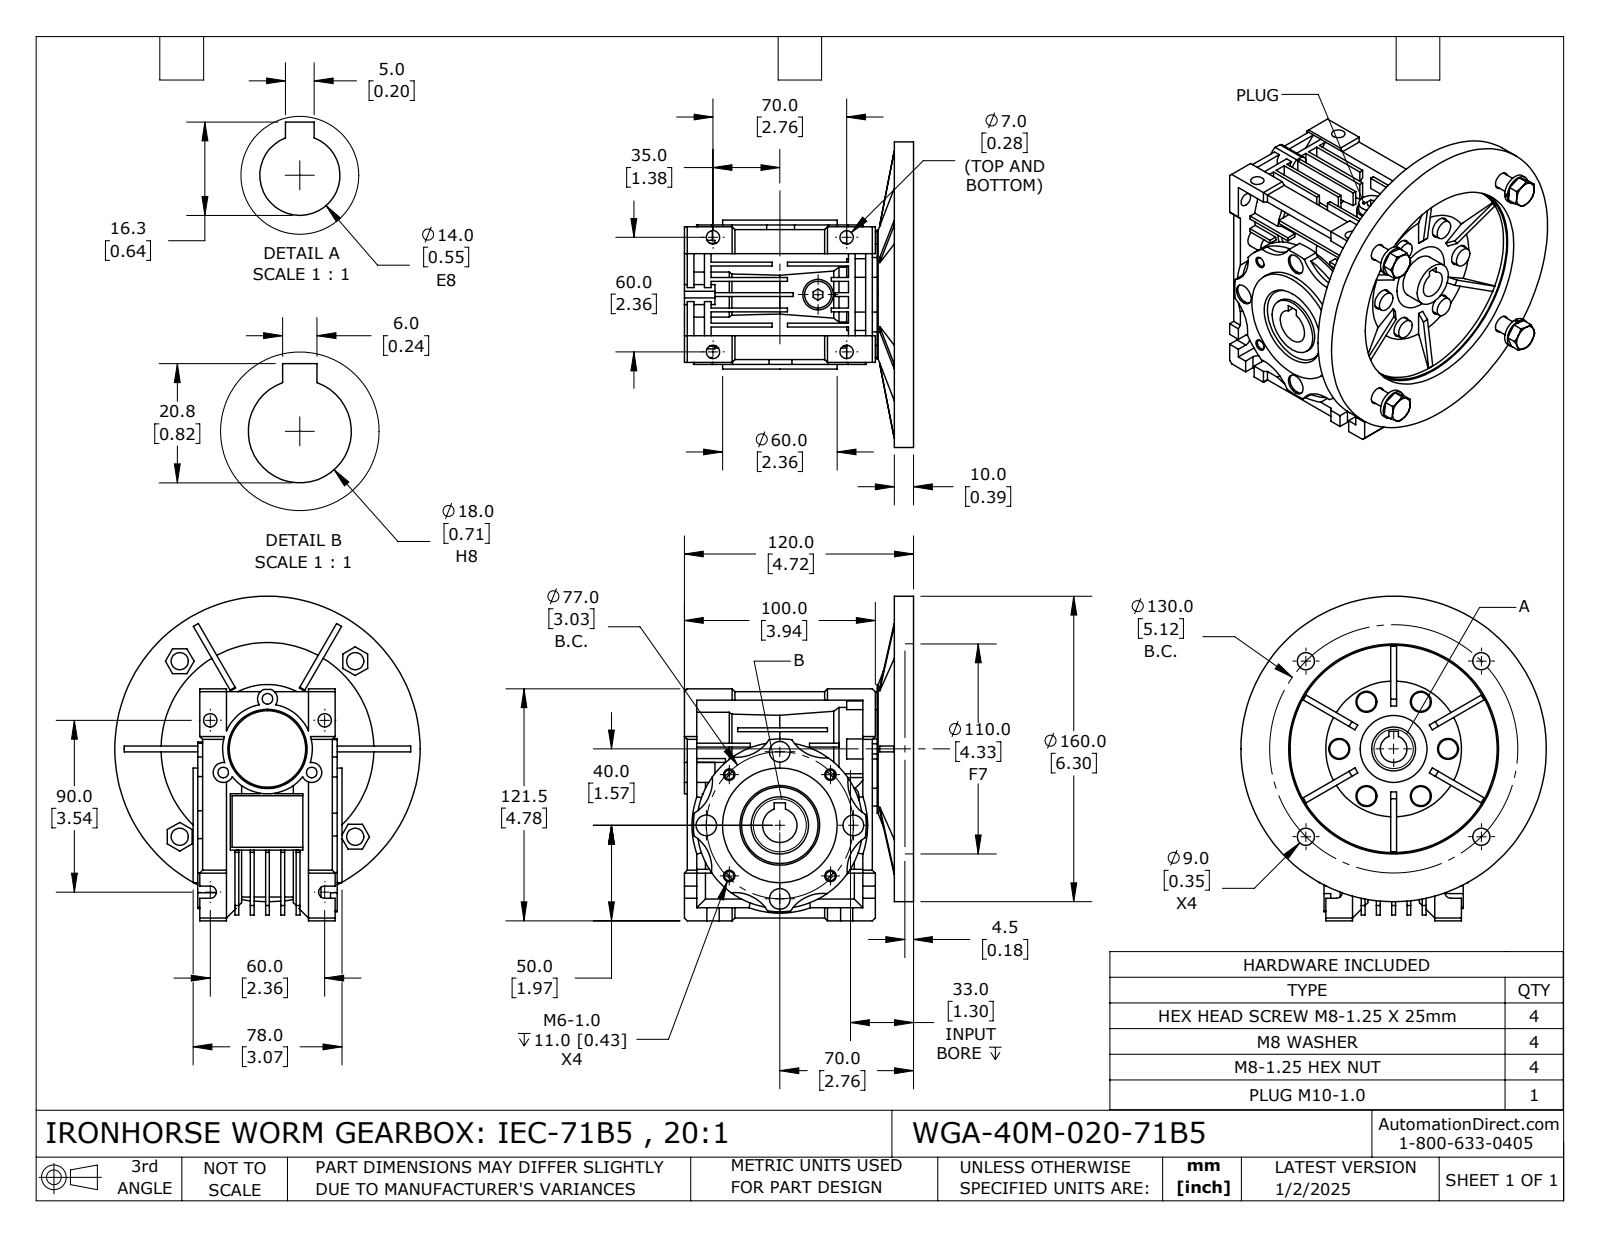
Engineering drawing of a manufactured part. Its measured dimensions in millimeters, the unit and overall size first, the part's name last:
Units: millimetres
Overall size (bounding box): 170 × 160 × 137.68
Round holes (diameter × count): ⌀7 ×6, ⌀11 ×6, ⌀9 ×5, ⌀4.92 ×4, ⌀6.8 ×4, ⌀8 ×4, ⌀8.2 ×4, ⌀10.8 ×4, ⌀5.55 ×3, ⌀14 ×1, ⌀15 ×1, ⌀18 ×1
Round bosses / shafts (diameter × count): ⌀10 ×6, ⌀15.4 ×4, ⌀160 ×1, ⌀75 ×1, ⌀67.5 ×1, ⌀60 ×1, ⌀54 ×1, ⌀47 ×1
Partial cylindrical surfaces — rounded edges, fillets, slot ends (radius × count): R20 ×8, R3.2 ×6, R5.22 ×6, R5.25 ×3, R43.5 ×1, R43.59 ×1, R45.25 ×1, R46 ×1
Main face-to-face distances: 10, 8, 2, 6, 5, 1.5, 16, 24, 14, 2.5
Hole centre spacings: 28.5, 29.1, 70.22, 49.36, 33.54, 37.5, 38.19, 38.5
Volume: 780 077 mm³ · Surface area: 202 021 mm²
Bodies: 18 solids, 1101 faces (630 planar, 290 cylindrical, 181 other)
Part name (STEP PRODUCT): WGA-40M-020-71B5
STEP written by: SolidWorks 2024 (CONFIG_CONTROL_DESIGN)
